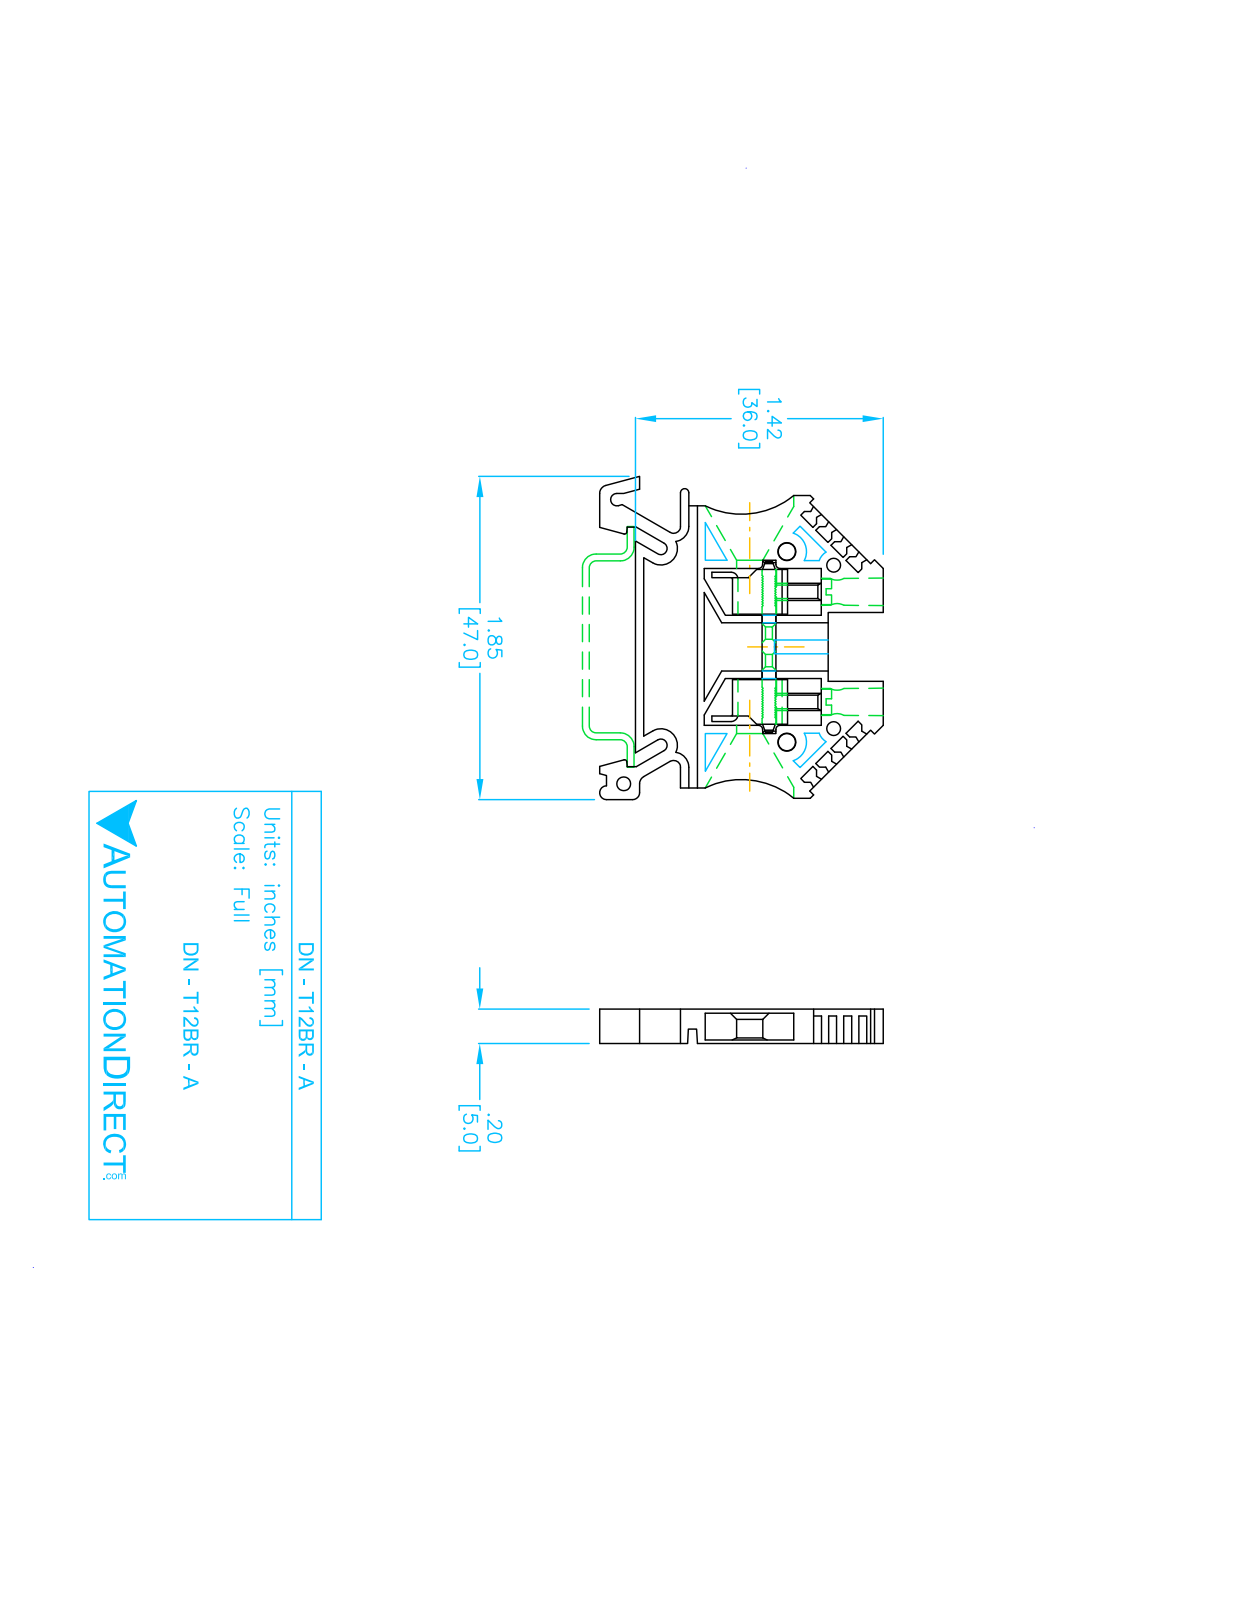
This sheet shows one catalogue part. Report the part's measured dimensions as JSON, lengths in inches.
{"part_name": "DN-T12BR-A", "step_written_by": "SolidWorks 2017 (AUTOMOTIVE_DESIGN)", "units": "inches", "bodies": {"solids": 1, "faces": 169, "planar": 134, "cylindrical": 35, "other": 0}, "overall_size": [1.85, 1.622, 0.197], "volume_in3": 0.306, "surface_area_in2": 7.131, "round_holes": [[0.164, 2], [0.079, 1]], "partial_cylinders_radius": [[0.039, 4], [0.035, 3], [0.012, 2], [0.047, 2], [0.087, 2], [0.094, 2], [0.472, 2], [0.024, 1]], "face_to_face_distances": [0.189, 0.197, 0.087, 0.02, 0.106, 0.094, 0.114, 0.083, 0.102, 0.354], "hole_center_spacings": [0.589]}
